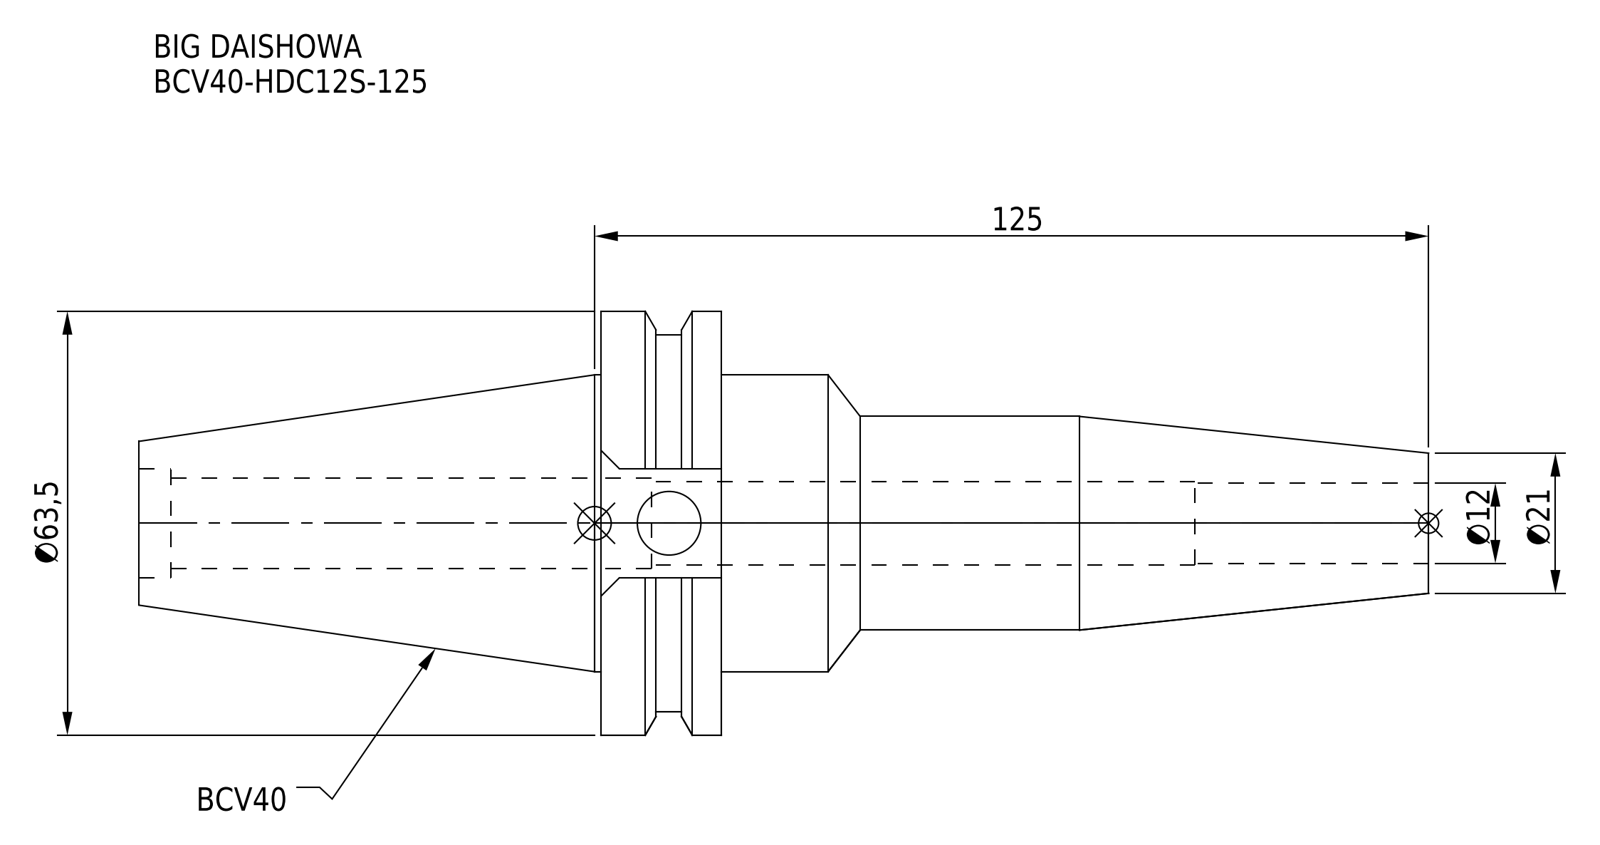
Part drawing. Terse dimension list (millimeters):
name: BCV40-HDC12S-125
written by: CREO PARAMETRIC BY PTC INC, 2016380 (AUTOMOTIVE_DESIGN)
unit: mm
bodies: 1 solid, 56 faces (22 planar, 24 cylindrical, 10 other)
size: 193.25 × 63.5 × 61.35
volume: 177 411 mm³; area: 34 239 mm²
holes: 1× ⌀9.53, 1× ⌀12, 1× ⌀12.5, 1× ⌀13.6, 1× ⌀16.32
bosses: 1× ⌀63.5, 1× ⌀56.36, 1× ⌀44.45, 1× ⌀32
face distances: 18.05, 87.3, 69.25, 105.95, 124, 193.25, 47.55, 16.38, 111.95, 6
